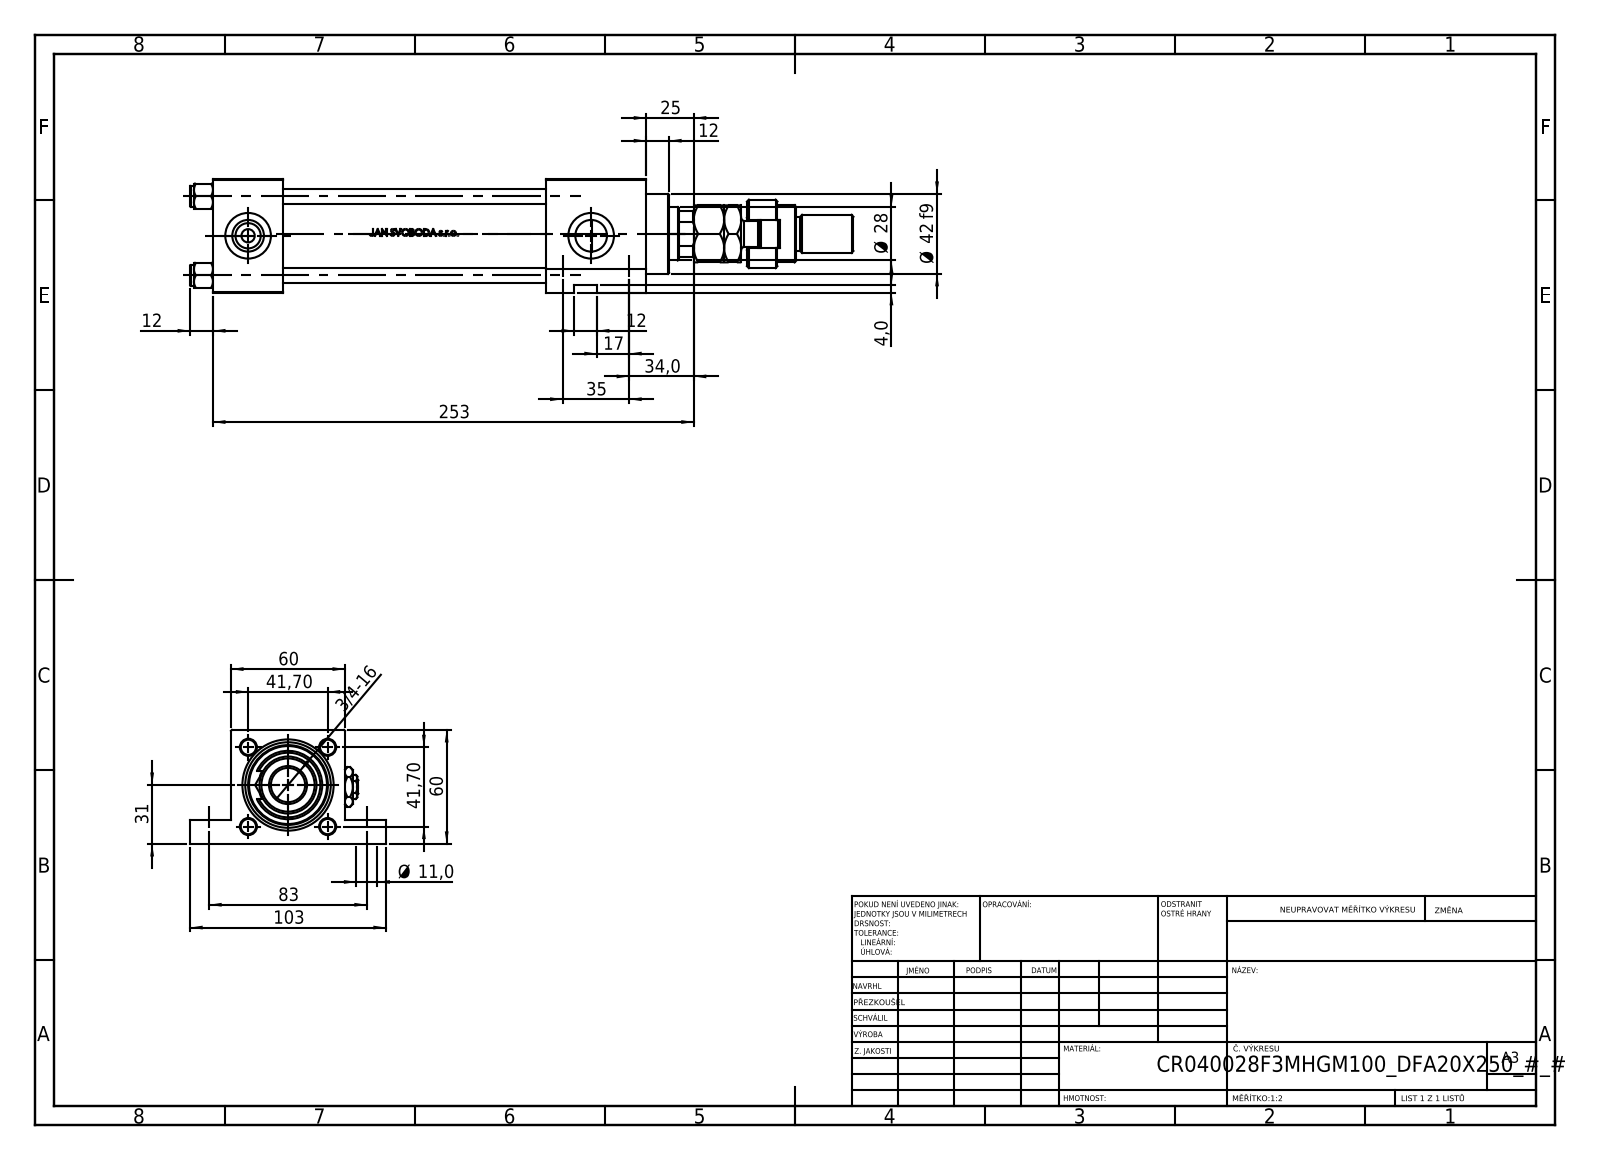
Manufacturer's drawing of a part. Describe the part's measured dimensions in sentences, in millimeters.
The part is named "Zatka_pro_OIL_PORT; NUT_M5_F; V215CR_F_TYCINKA; FEMALE_PART_FOR_DFA (+4 more)". Its 3-D file was written by "SolidWorks 2019 (CONFIG_CONTROL_DESIGN)". It is 15 solids with 1300 faces: 512 planar, 162 cylindrical and 626 other. Overall it measures 349 by 103 by 60 millimeters. Its volume is 588 447 cubic millimeters and its surface area 170 561 square millimeters. Round holes: 4 of diameter 8, 4 of diameter 11, 3 of diameter 16.66, 3 of diameter 24, 2 of diameter 7, 1 of diameter 16, 1 of diameter 18.5, 1 of diameter 28, 1 of diameter 31, 1 of diameter 40, 1 of diameter 45. Round bosses or shafts: 4 of diameter 11, 1 of diameter 46, 1 of diameter 42, 1 of diameter 36, 1 of diameter 30, 1 of diameter 22, 1 of diameter 20, 1 of diameter 18. Partial cylindrical surfaces (rounded edges, fillets, slot ends): 1 of radius 7.5, 1 of radius 12, 1 of radius 13.5. The main face-to-face distances are 60, 37, 53, 175, 138, 228, 38, 191, 12.5, 47.5. The hole center spacings are 41.7, 28.79, 30.2, 35, 58.97, 83, 90.08, 8.
